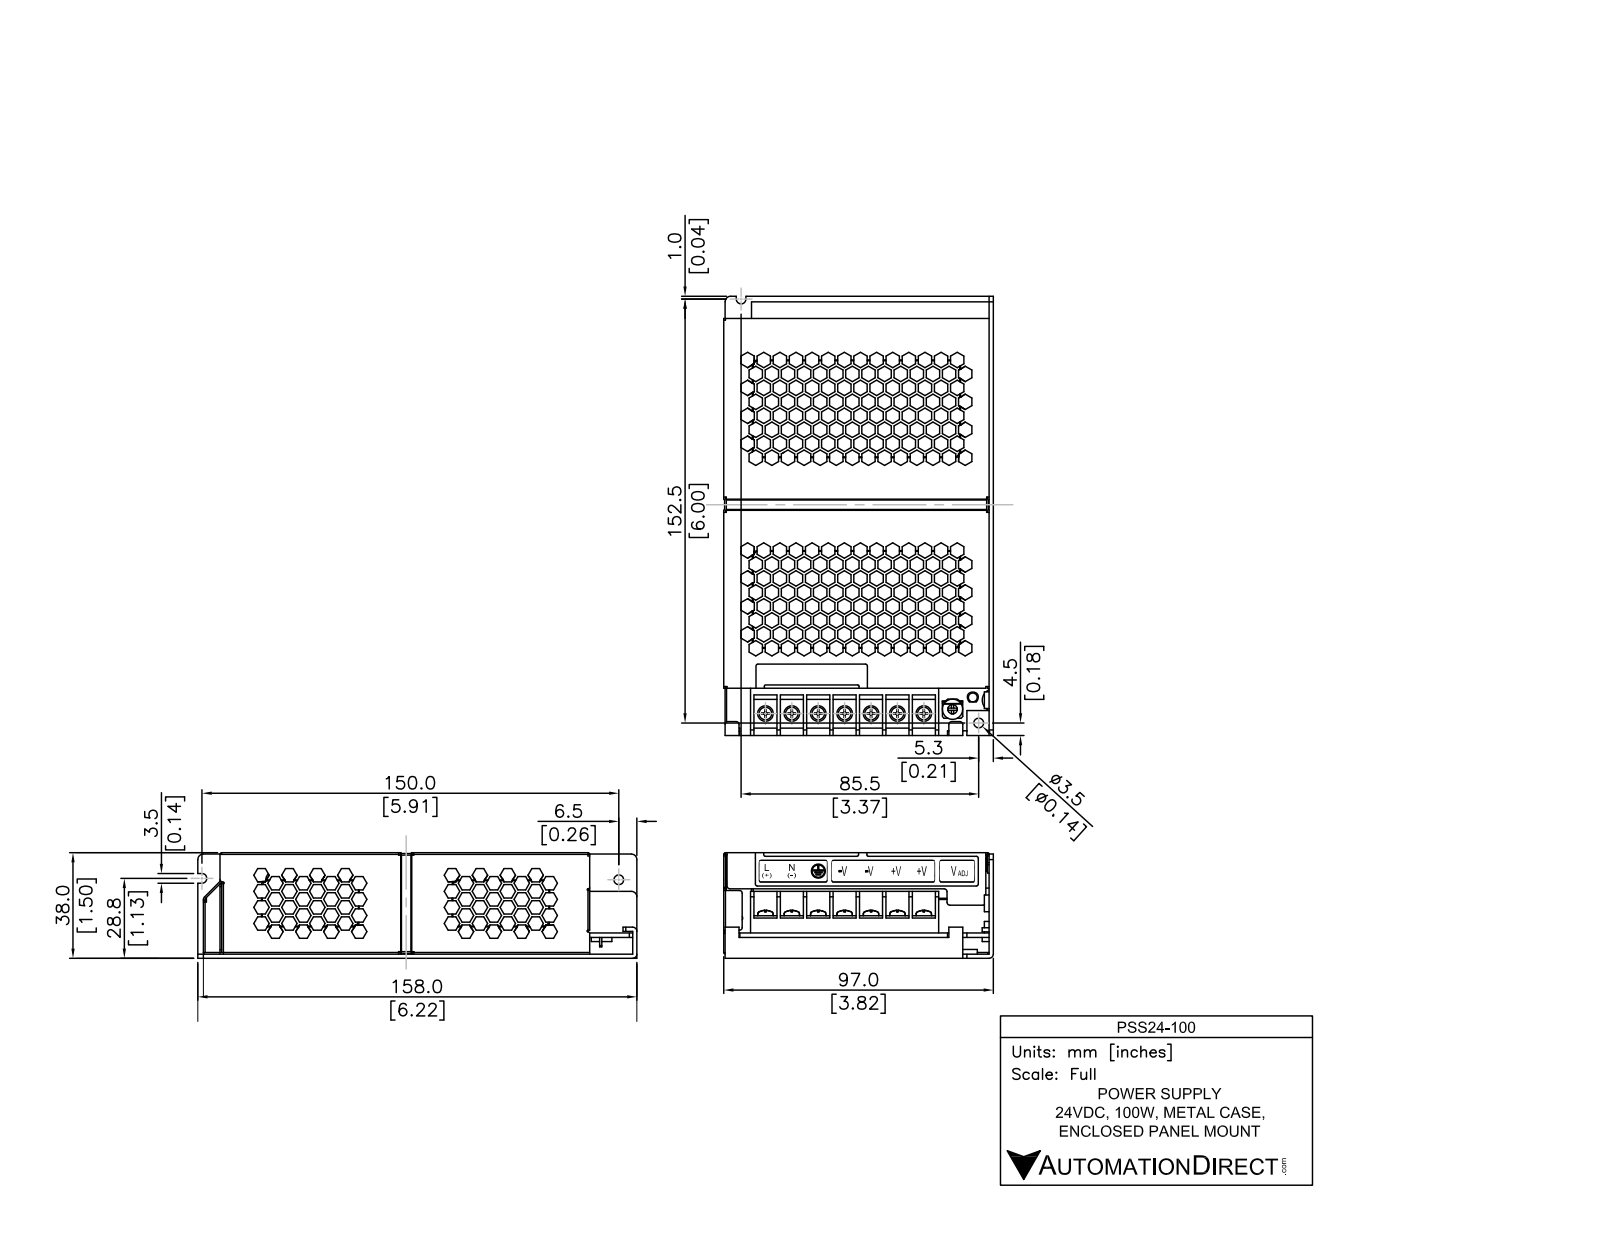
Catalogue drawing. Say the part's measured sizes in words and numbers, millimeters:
The part is named "PSS 24-100". Its 3-D file was written by "SolidWorks 2011 (CONFIG_CONTROL_DESIGN)". It is 3 solids with 2250 faces: 2101 planar, 73 cylindrical and 76 other. Overall it measures 158 by 97 by 38.1 millimeters. Its volume is 172 600 cubic millimeters and its surface area 119 300 square millimeters. Round holes: 2 of diameter 3.3. Round bosses or shafts: 7 of diameter 5.6, 2 of diameter 0.7, 1 of diameter 7, 1 of diameter 3.1, 1 of diameter 1.8, 1 of diameter 1.7. Partial cylindrical surfaces (rounded edges, fillets, slot ends): 7 of radius 0.8, 5 of radius 1, 5 of radius 1.3, 4 of radius 1.5, 2 of radius 0.4, 2 of radius 1.8, 2 of radius 4.4, 1 of radius 2.5. The main face-to-face distances are 0.8, 37.3, 9.8, 8.3, 7.5, 27.6, 36.6, 29, 38.1, 29.8.
